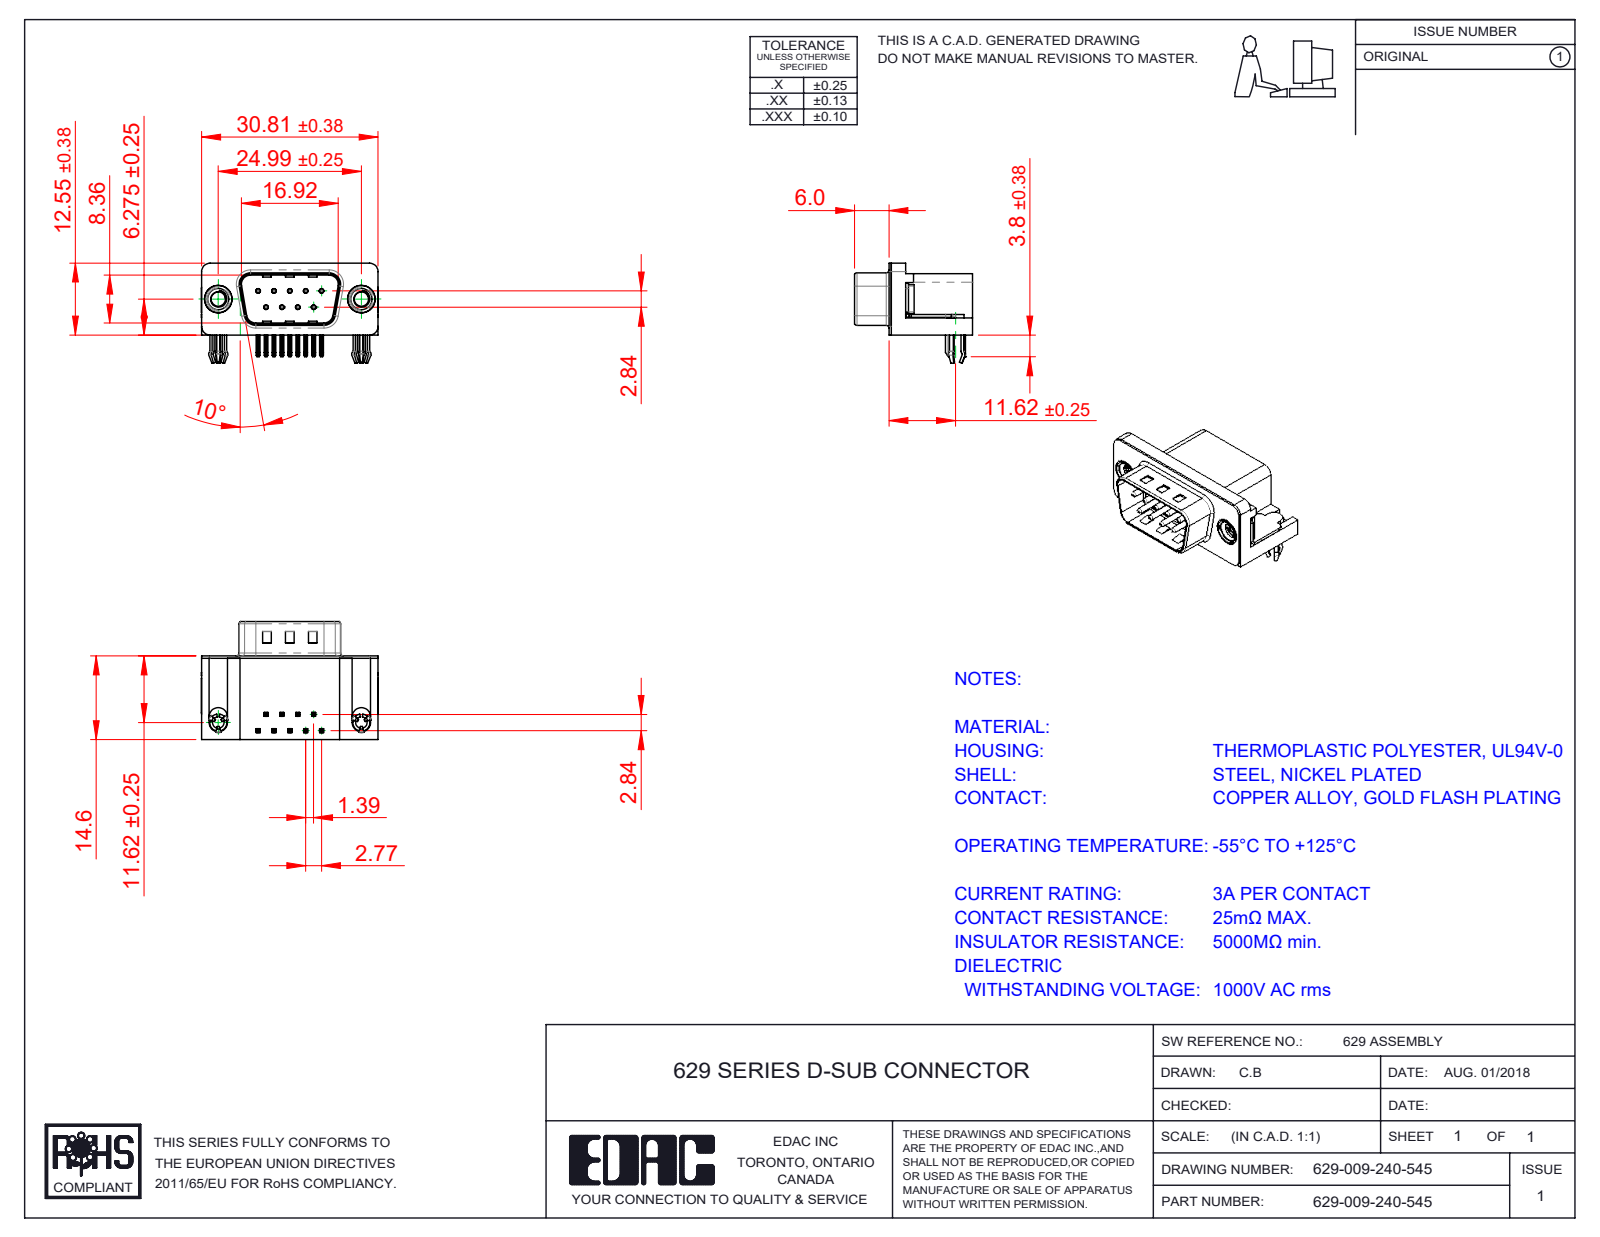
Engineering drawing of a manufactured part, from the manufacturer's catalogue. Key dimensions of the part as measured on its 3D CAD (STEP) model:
Part name (STEP PRODUCT): 629 Contact Bottom; 629 M3 Threaded Rivet; 629 Contact Top; 629 3 Prong Board Lock (+3 more)
STEP written by: SolidWorks 2020 (CONFIG_CONTROL_DESIGN)
Units: millimetres
Bodies: 15 solids, 1093 faces (609 planar, 325 cylindrical, 159 other)
Overall size (bounding box): 30.89 × 20.6 × 17.48
Volume: 3 725 mm³ · Surface area: 4 822 mm²
Round holes (diameter × count): ⌀0.35 ×9, ⌀0.8 ×9, ⌀2 ×2, ⌀2.5 ×2, ⌀4 ×2, ⌀4.8 ×2, ⌀5 ×2
Round bosses / shafts (diameter × count): ⌀0.75 ×9, ⌀4.9 ×2, ⌀4.75 ×2, ⌀3.9 ×2, ⌀3 ×2
Partial cylindrical surfaces — rounded edges, fillets, slot ends (radius × count): R0.25 ×48, R0.12 ×18, R1 ×16, R0.5 ×9, R1.5 ×8, R1.6 ×8, R0.9 ×4, R2 ×4
Main face-to-face distances: 0.4, 14.2, 10.35, 14.6, 0.5, 2.9, 11.7, 2.5, 2.1, 6.7
Hole centre spacings: 3.16, 2.77, 5.54, 5.03, 5.04, 8.31, 7.48, 7.49
